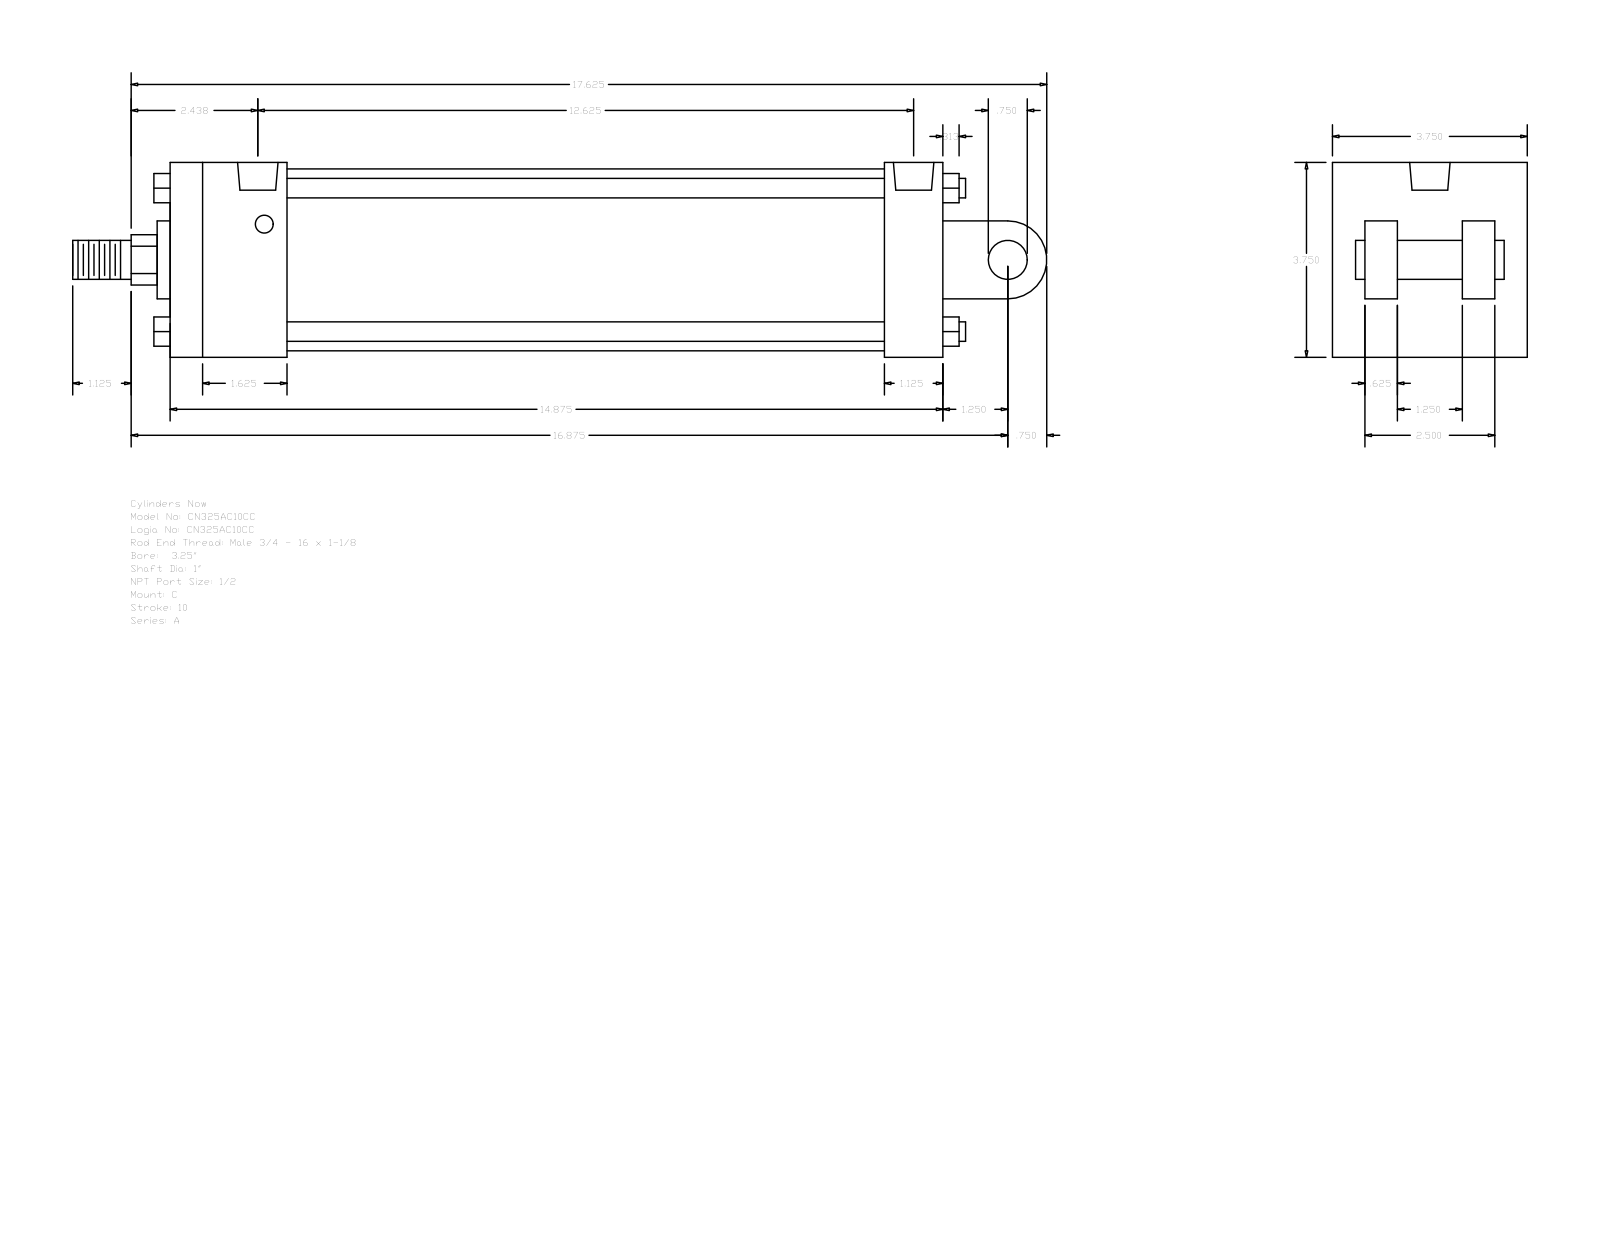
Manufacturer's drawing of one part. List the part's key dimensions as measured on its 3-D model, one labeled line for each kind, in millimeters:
Part name (STEP PRODUCT): A_C__0325_1
STEP written by: GSSL Pune (CONFIG_CONTROL_DESIGN)
Units: millimetres
Bodies: 0 solids, 135 faces (102 planar, 33 cylindrical, 0 other)
Overall size (bounding box): 476.25 × 95.25 × 95.25
Round holes (diameter × count): ⌀8.73 ×4, ⌀19.77 ×2
Round bosses / shafts (diameter × count): ⌀9.53 ×4, ⌀19.05 ×2, ⌀88.9 ×1, ⌀38.1 ×1, ⌀25.4 ×1
Partial cylindrical surfaces — rounded edges, fillets, slot ends (radius × count): R12.29 ×1, R19.05 ×1
Main face-to-face distances: 95.24, 377.83, 15.87, 63.5, 79.37, 31.74, 47.63, 66.67, 349.25, 28.58
Hole centre spacings: 3.18, 314.32, 317.5, 320.68
